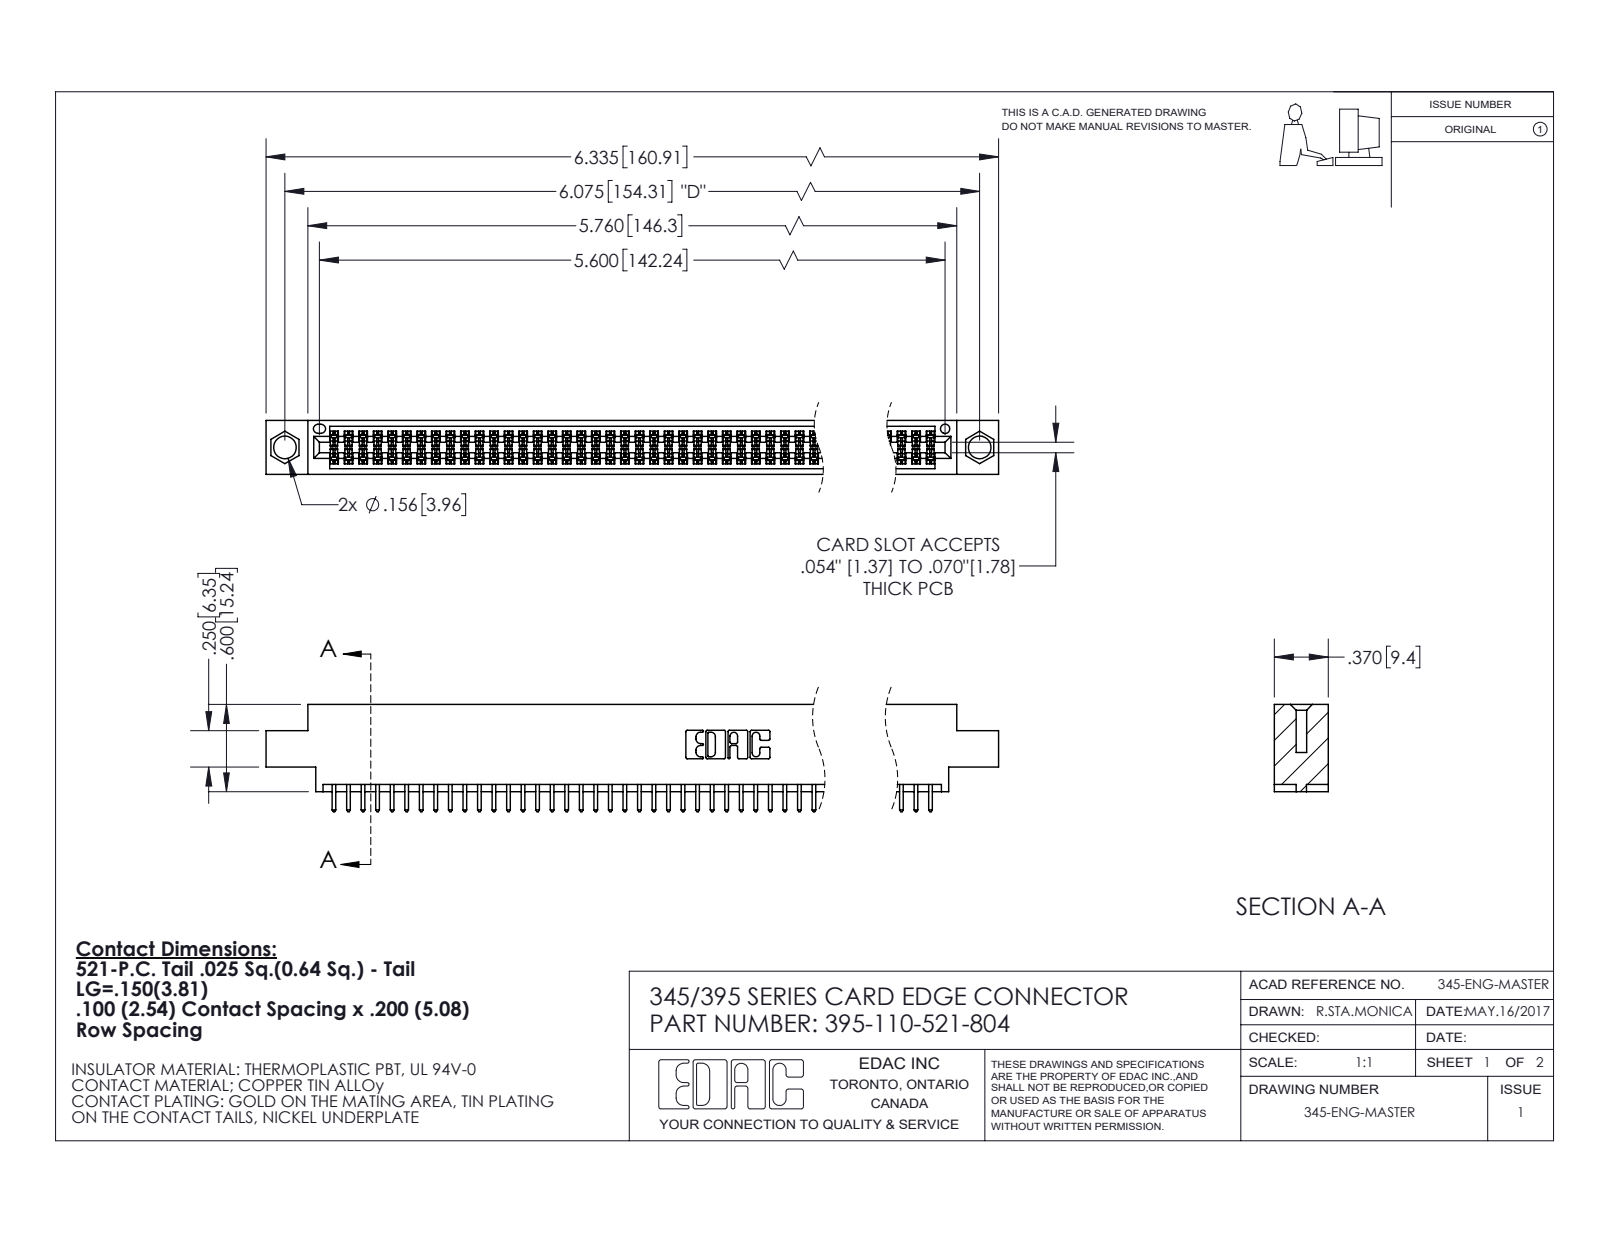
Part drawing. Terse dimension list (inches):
name: 345 Part_0.170 Offset - 0.156 Dia-TI; 395-110-521-804; 345-292-001_345-293-121
written by: SolidWorks 2020 (CONFIG_CONTROL_DESIGN)
unit: in
bodies: 111 solids, 5644 faces (3728 planar, 1916 cylindrical, 0 other)
size: 6.335 × 0.737 × 0.37
volume: 0.945 in³; area: 35.41 in²
holes: 2× ⌀0.156, 1× ⌀0.064
rounds: 219× R0.006, 110× R0.01, 22× R0.01, 6× R0.007, 6× R0.031, 3× R0.026, 2× R0.014, 2× R0.019
face distances: 0.072, 0.298, 0.2, 0.37, 0.098, 0.272, 0.025, 0.225, 0.175, 0.149
hole spacings: 0.27, 5.839, 6.075
